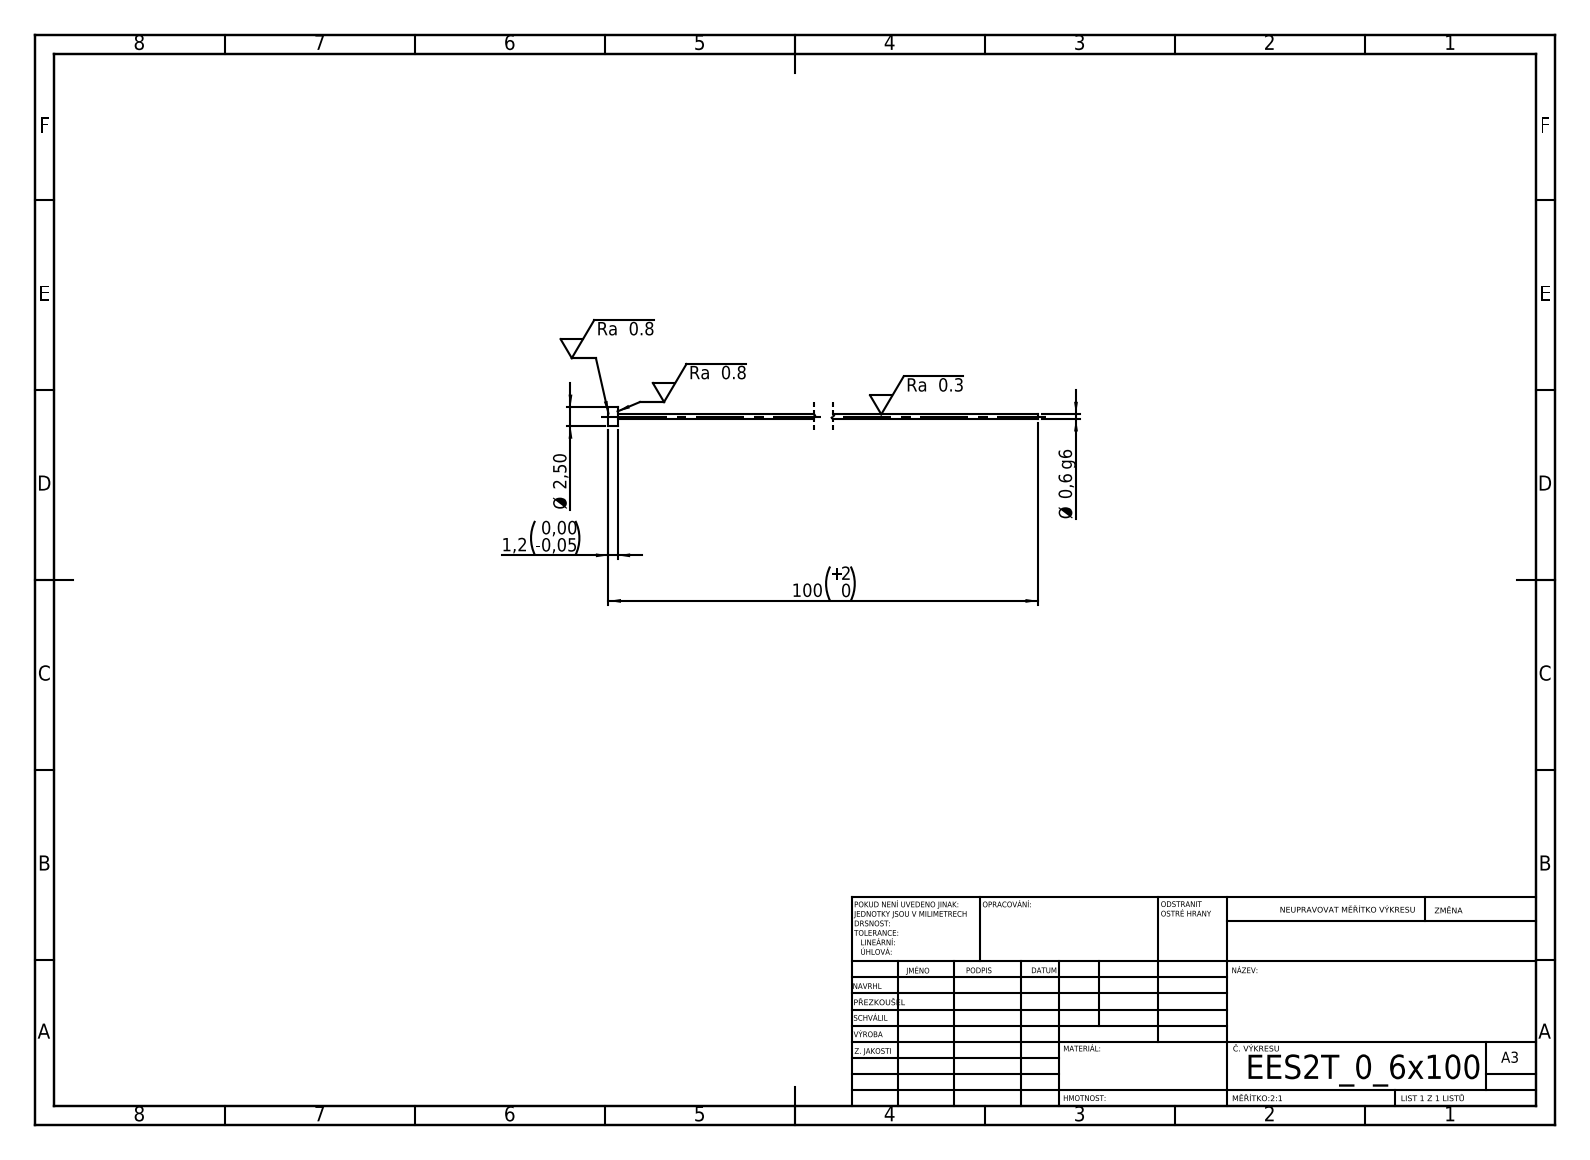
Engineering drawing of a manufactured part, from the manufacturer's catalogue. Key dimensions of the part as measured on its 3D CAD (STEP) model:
STEP written by: SolidWorks 2019 (CONFIG_CONTROL_DESIGN)
Units: millimetres
Bodies: 1 solid, 7 faces (3 planar, 4 cylindrical, 0 other)
Overall size (bounding box): 100 × 2.5 × 2.5
Volume: 34 mm³ · Surface area: 205 mm²
Round bosses / shafts (diameter × count): ⌀2.5 ×1, ⌀0.6 ×1
Main face-to-face distances: 1.2, 100, 98.8
